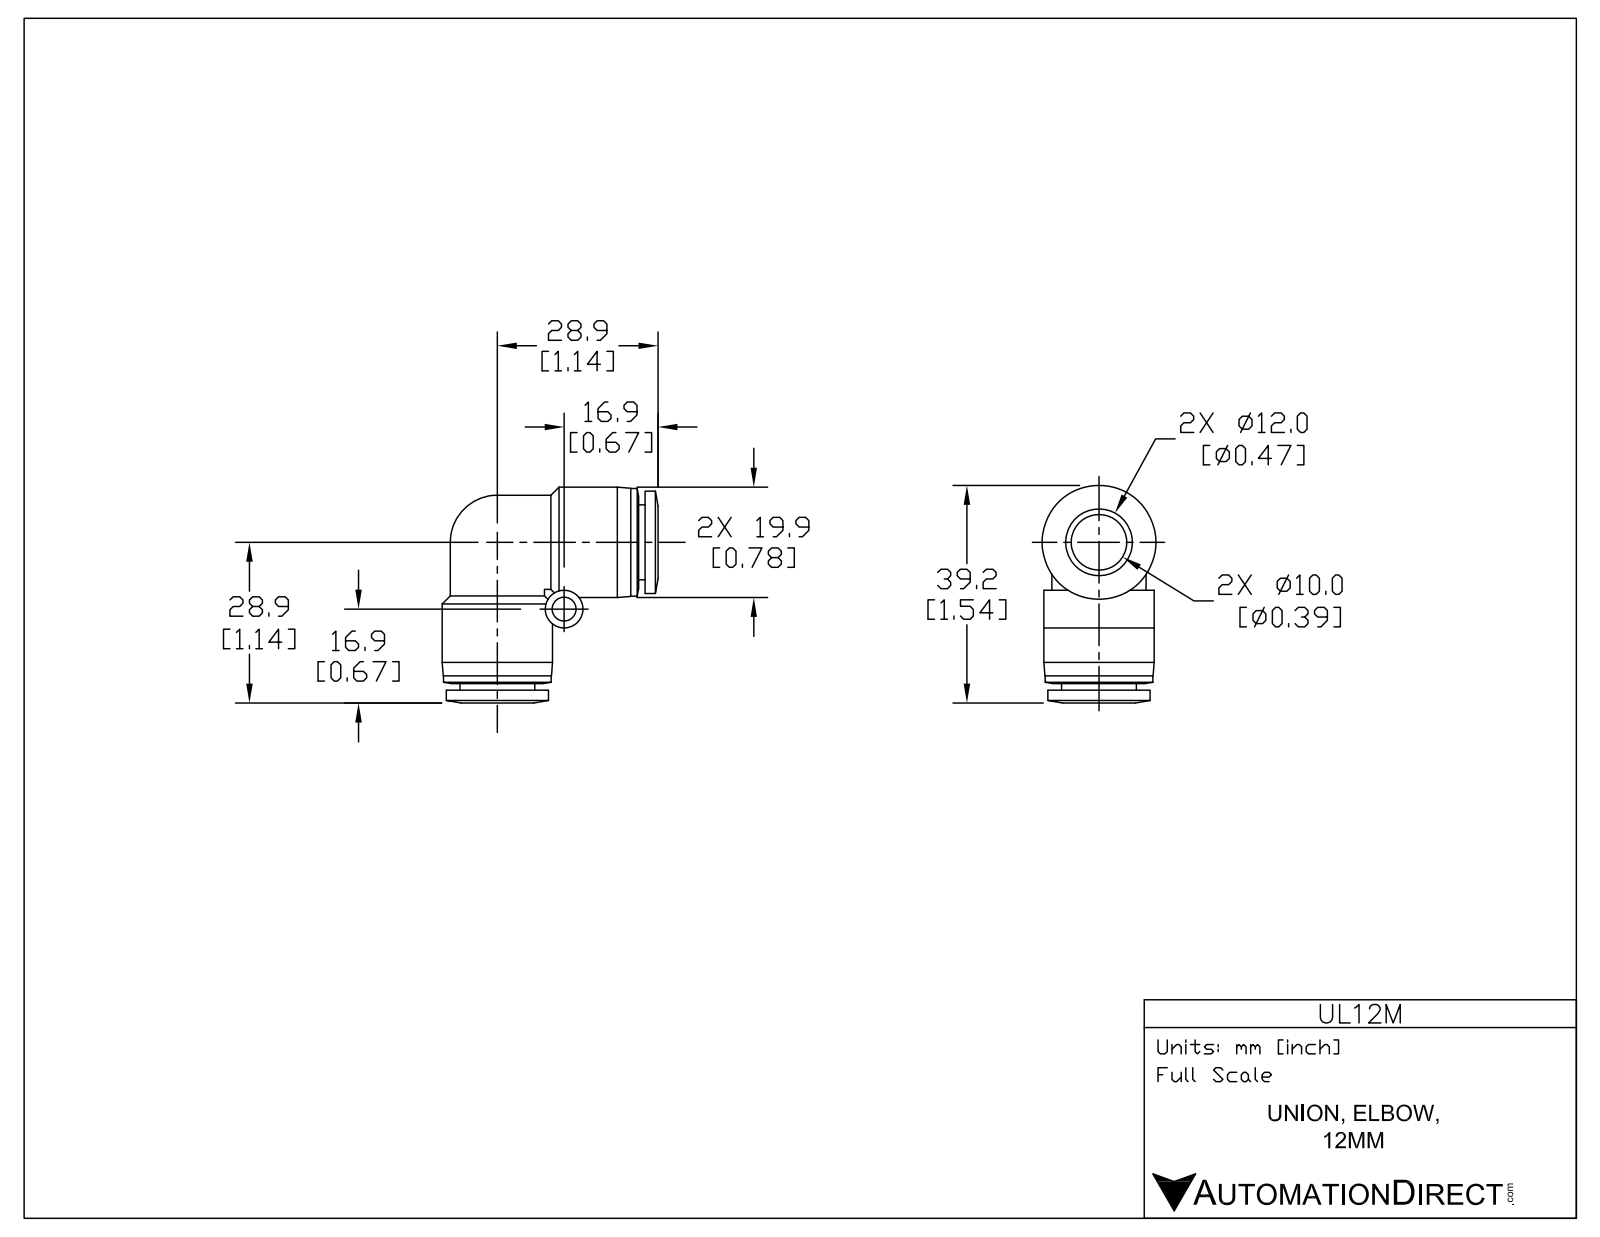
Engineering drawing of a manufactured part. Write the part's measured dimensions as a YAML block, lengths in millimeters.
part_name: "UL12M"
step_written_by: "SolidWorks 2015 (AUTOMOTIVE_DESIGN)"
units: millimeters
bodies: {solids: 1, faces: 68, planar: 12, cylindrical: 32, other: 24}
overall_size: [40.1, 40.1, 20.5]
volume: 10700
surface_area: 7277
round_holes:
  - {diameter: 10, count: 2}
  - {diameter: 12.3, count: 2}
  - {diameter: 4.3, count: 1}
round_bosses_or_shafts:
  - {diameter: 20.5, count: 2}
  - {diameter: 20, count: 2}
  - {diameter: 19, count: 2}
  - {diameter: 17.5, count: 2}
  - {diameter: 13.9, count: 2}
  - {diameter: 7, count: 1}
face_to_face_distances: [1.2, 20.5, 19.3, 22.9, 3.6, 2.4, 17.9, 1.4, 2.6, 5.1]
